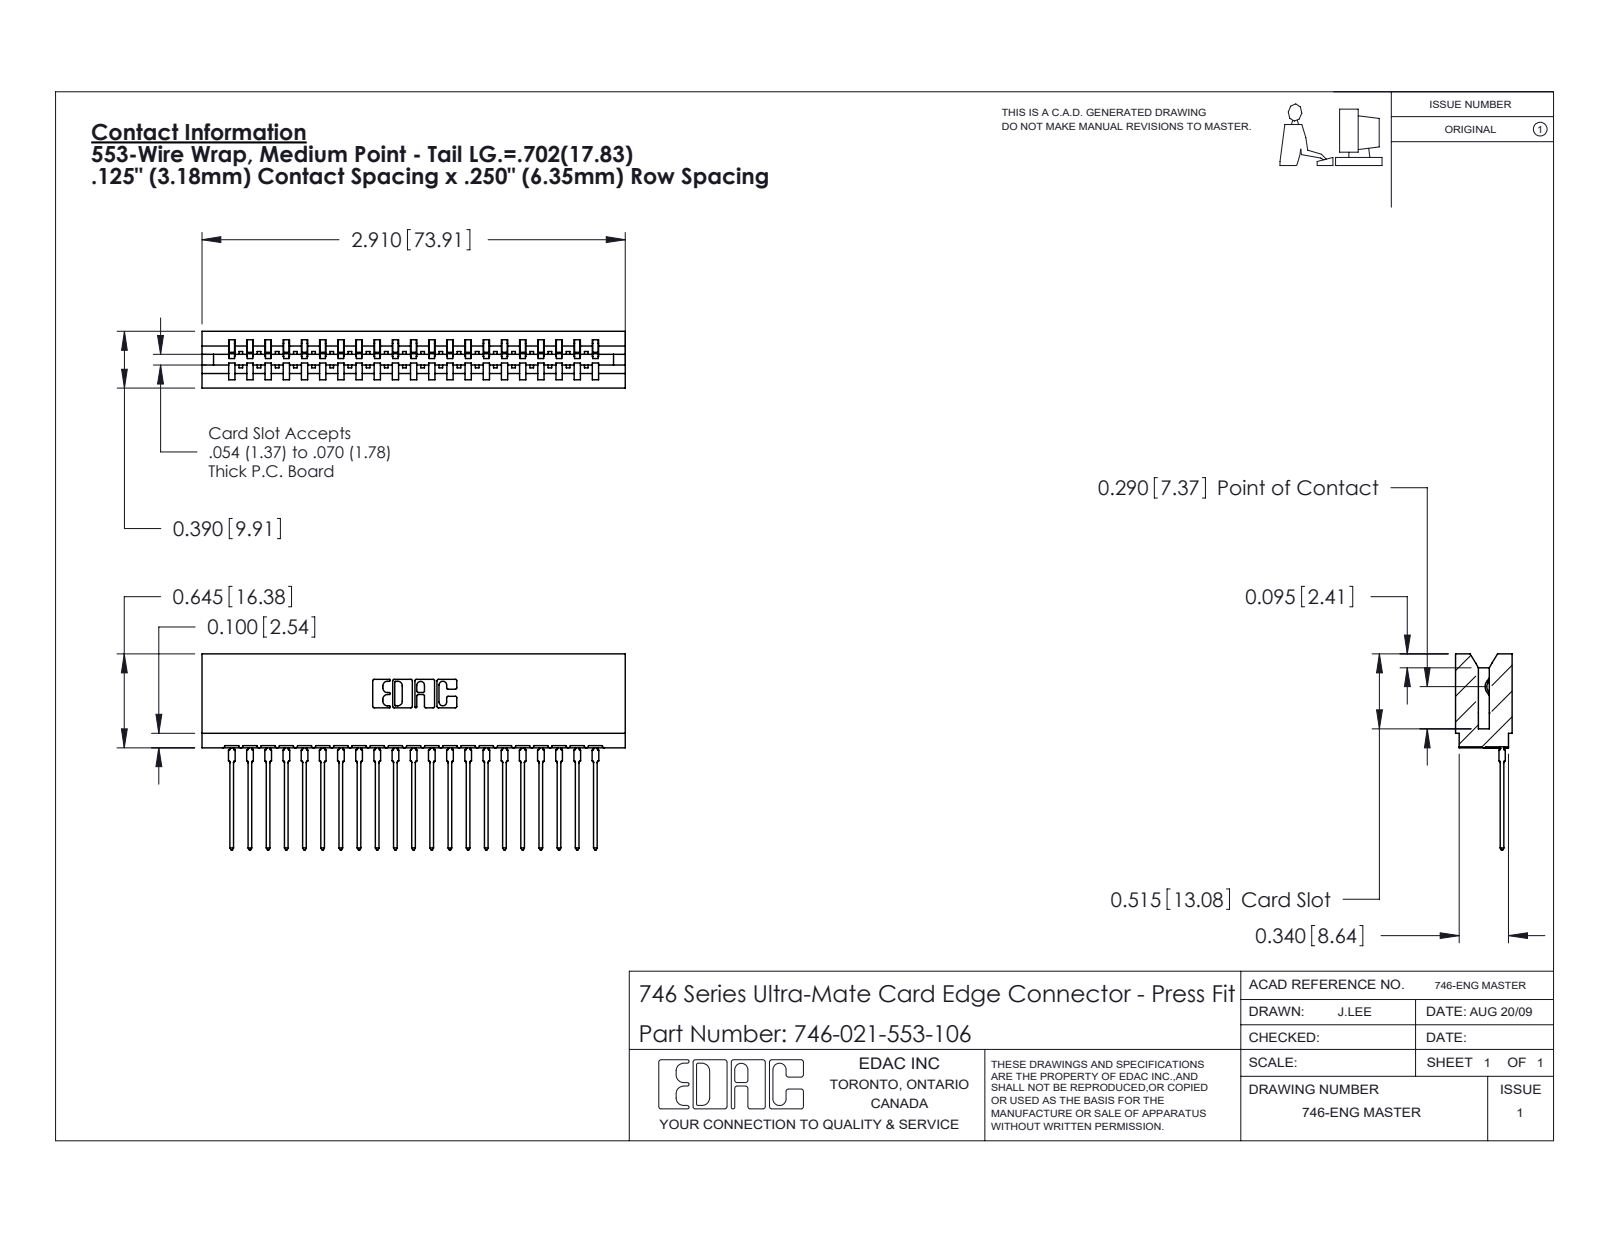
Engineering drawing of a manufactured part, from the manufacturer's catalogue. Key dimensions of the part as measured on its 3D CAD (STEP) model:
Part name (STEP PRODUCT): 746 Part_.515 Slot Depth - 06; 746-021-553-106; 746-292-001_553
STEP written by: SolidWorks 2020 (CONFIG_CONTROL_DESIGN)
Units: inches
Bodies: 22 solids, 2366 faces (1379 planar, 441 cylindrical, 546 other)
Overall size (bounding box): 2.91 × 1.346 × 0.39
Volume: 0.483 in³ · Surface area: 18.29 in²
Partial cylindrical surfaces — rounded edges, fillets, slot ends (radius × count): R0.021 ×42, R0.01 ×22, R0.015 ×22, R0.007 ×6, R0.031 ×6, R0.005 ×4, R0.011 ×4, R0.026 ×3
Main face-to-face distances: 0.057, 0.333, 0.25, 0.39, 0.5, 0.025, 0.307, 0.083, 0.042, 0.125
